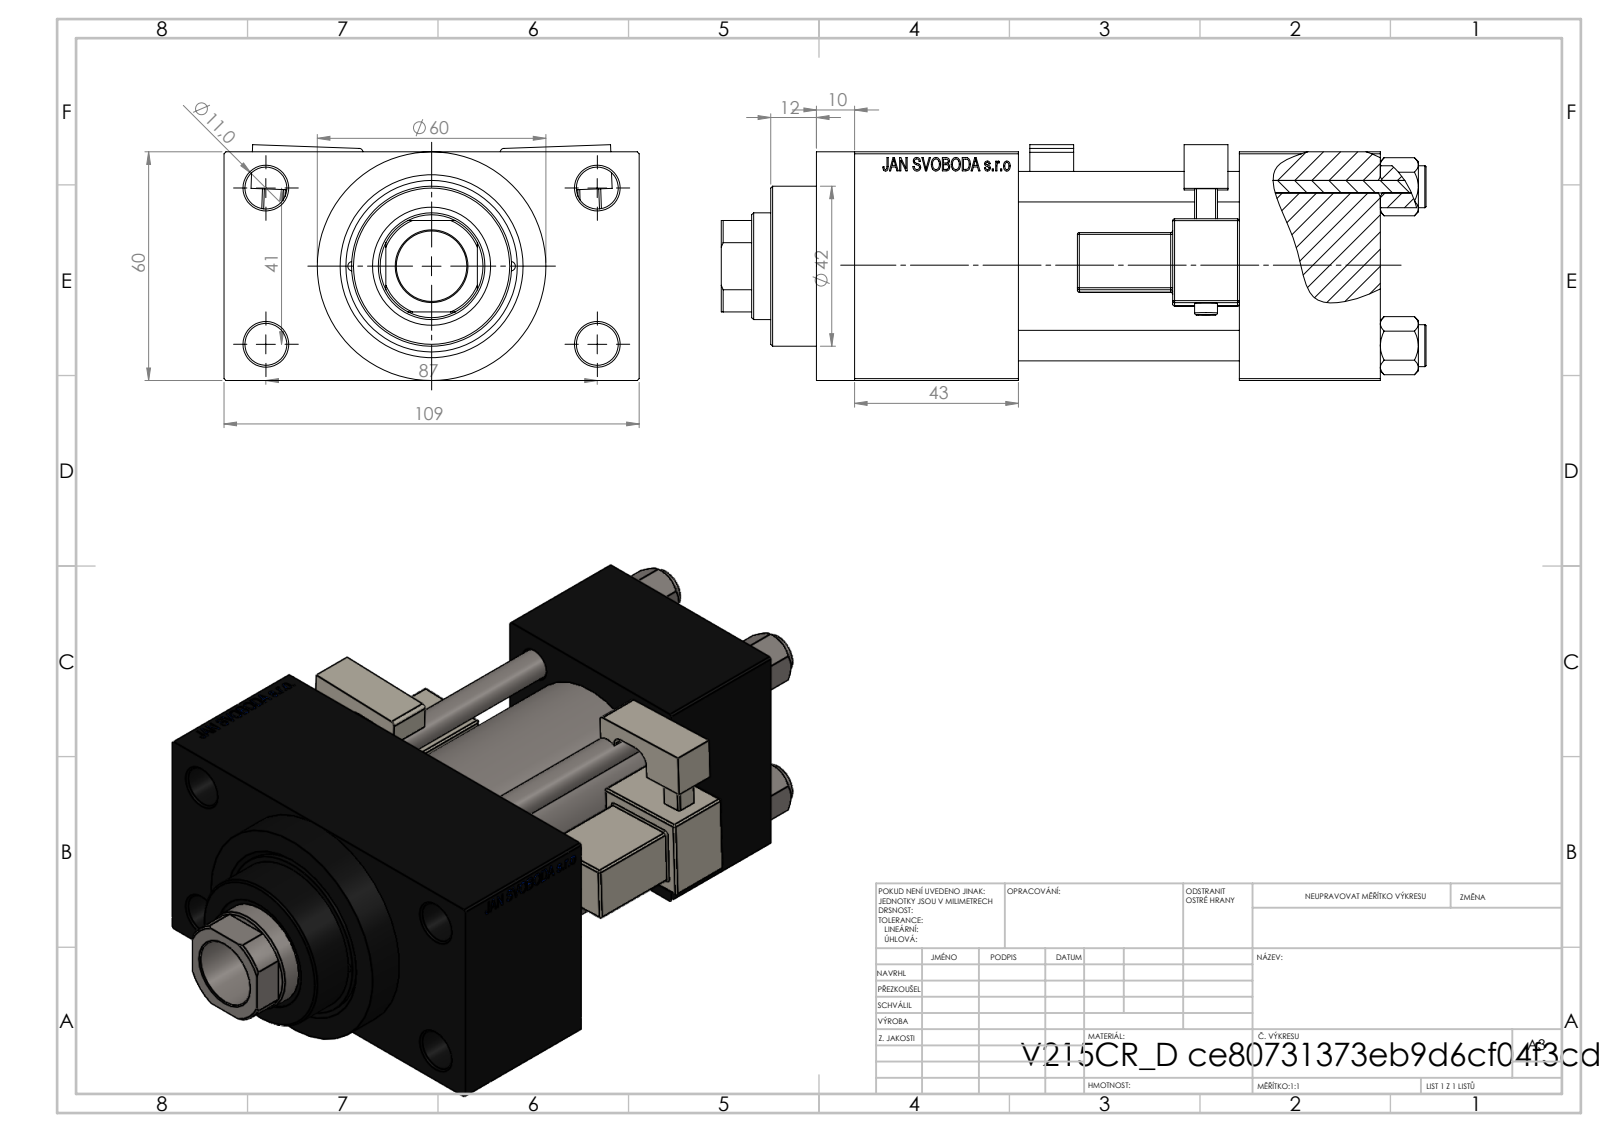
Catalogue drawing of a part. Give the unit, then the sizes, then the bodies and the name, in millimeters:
Units: millimetres
Overall size (bounding box): 185 × 109 × 61.9
Round holes (diameter × count): ⌀8 ×4, ⌀11 ×4, ⌀2.5 ×2, ⌀7 ×2, ⌀16.66 ×2, ⌀24 ×2, ⌀18.5 ×1, ⌀28 ×1, ⌀31 ×1, ⌀40 ×1, ⌀45 ×1
Round bosses / shafts (diameter × count): ⌀11 ×4, ⌀6 ×2, ⌀60 ×1, ⌀46 ×1, ⌀42 ×1
Partial cylindrical surfaces — rounded edges, fillets, slot ends (radius × count): R0.5 ×48, R1 ×2, R2.5 ×2, R4 ×2, R13.5 ×1
Main face-to-face distances: 60, 58, 24.5, 84.5, 37, 95, 138, 101, 43, 109
Hole centre spacings: 20.85, 22.65, 29.49, 30.62, 41.7, 46.53, 47.15, 48.09
Volume: 569 501 mm³ · Surface area: 141 163 mm²
Bodies: 13 solids, 1268 faces (560 planar, 152 cylindrical, 556 other)
Part name (STEP PRODUCT): V215CR_VCP_D; V215_VC_A; V215CR_D_Body; NUT_M5_D (+2 more)
STEP written by: SolidWorks 2019 (CONFIG_CONTROL_DESIGN)
